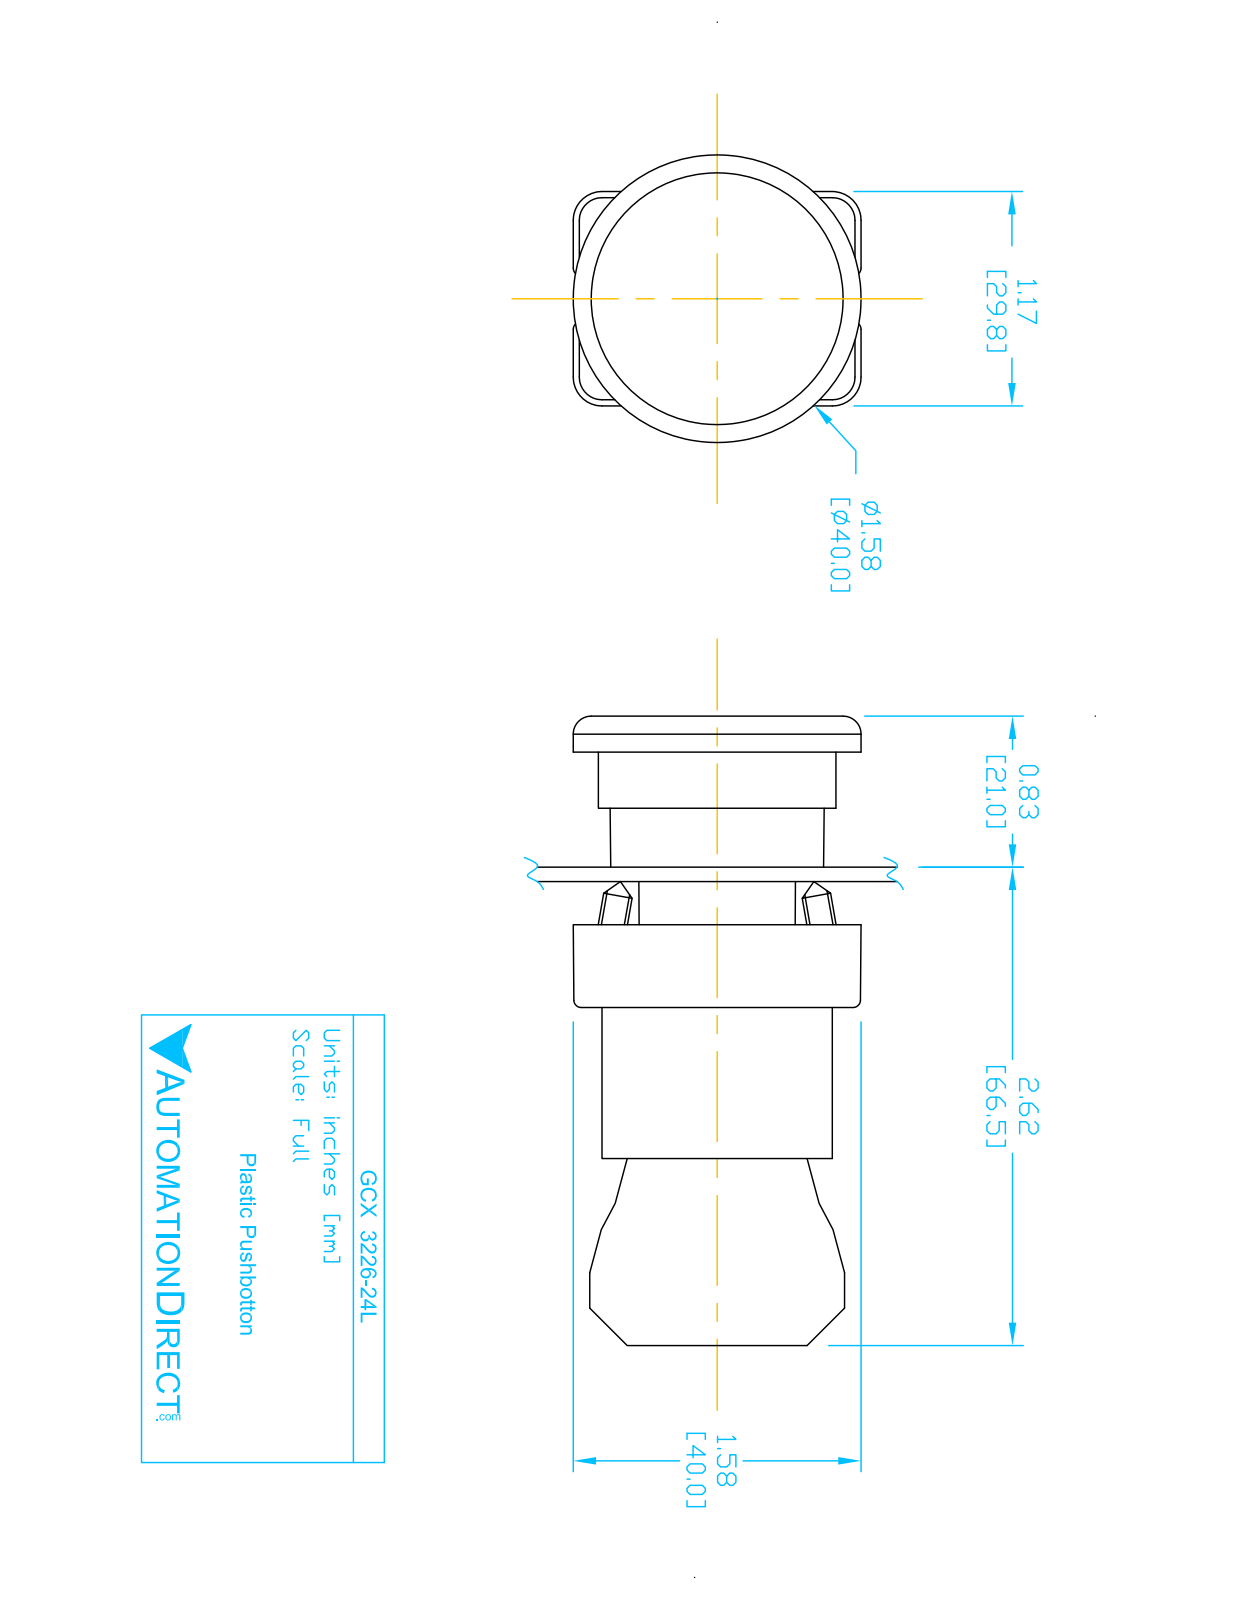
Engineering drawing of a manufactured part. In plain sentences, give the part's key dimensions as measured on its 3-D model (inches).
The part is named "ecx1030; ECX1050; GCX322X OPERATOR; GCX3226-24L (+1 more)". Its 3-D file was written by "SolidWorks 2016 (AUTOMOTIVE_DESIGN)". It is 7 solids with 431 faces: 252 planar, 146 cylindrical and 33 other. Overall it measures 3.469 by 1.581 by 1.575 inches. Its volume is 2.895 cubic inches and its surface area 40.89 square inches. Round holes: 2 of diameter 0.079, 2 of diameter 0.124, 2 of diameter 0.13, 1 of diameter 0.087, 1 of diameter 0.197, 1 of diameter 0.469, 1 of diameter 0.878, 1 of diameter 0.888, 1 of diameter 1.024, 1 of diameter 1.181. Round bosses or shafts: 4 of diameter 0.157, 1 of diameter 1.299, 1 of diameter 1.175, 1 of diameter 0.945, 1 of diameter 0.856, 1 of diameter 0.78, 1 of diameter 0.504. Partial cylindrical surfaces (rounded edges, fillets, slot ends): 24 of radius 0.059, 12 of radius 0.041, 12 of radius 0.124, 12 of radius 0.157, 8 of radius 0.039, 2 of radius 0.128, 1 of radius 0.02, 1 of radius 0.063. The main face-to-face distances are 0.827, 2.445, 1.618, 0.579, 2.287, 1.461, 0.157, 0.587, 0.031, 1.165. The hole center spacings are 0.236, 0.539, 0.472, 0.484.
